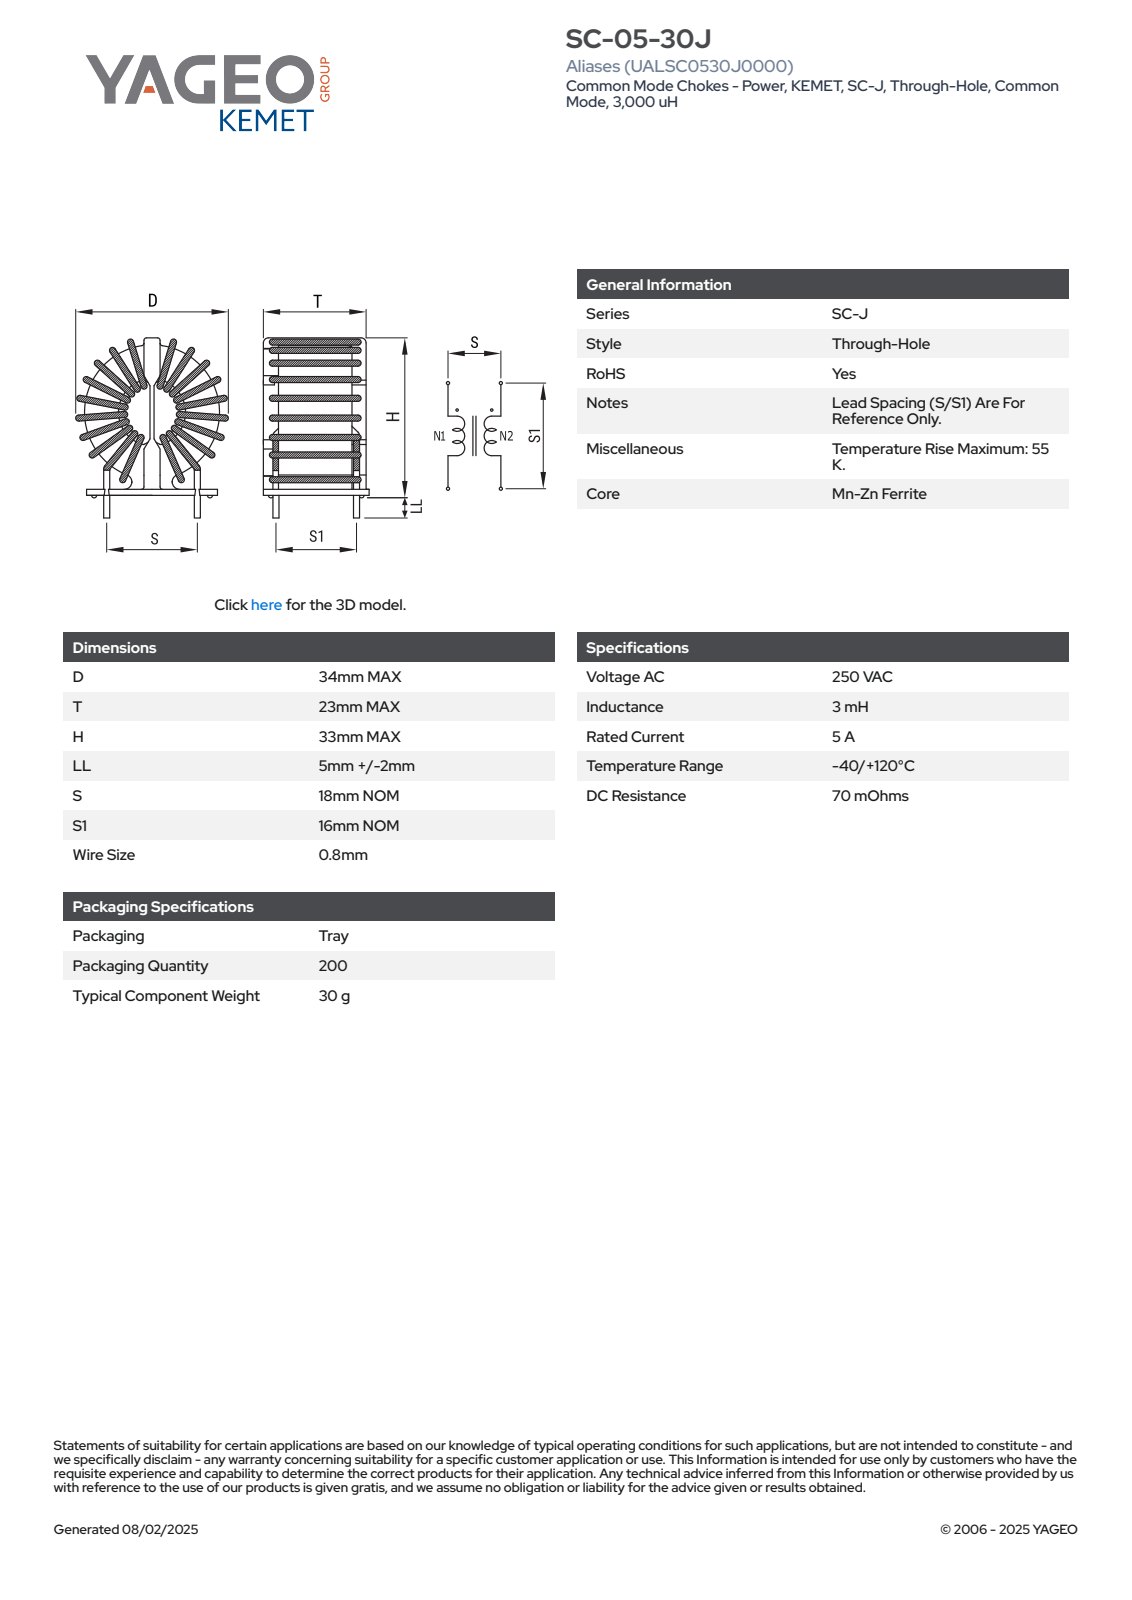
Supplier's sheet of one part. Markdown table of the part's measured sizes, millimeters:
| quantity | value |
| --- | --- |
| part name | SC-05-30J |
| STEP written by | SolidWorks 2018 (AUTOMOTIVE_DESIGN) |
| units | millimeters |
| bodies | 1 solid, 393 faces (177 planar, 132 cylindrical, 84 other) |
| overall size | 38 × 34 × 23 |
| volume | 14 501 mm³ |
| surface area | 7 757 mm² |
| round holes (diameter × count) | 1 × 4 |
| round bosses / shafts (diameter × count) | 0.8 × 8, 1 × 4 |
| partial cylindrical surfaces (radius × count) | 0.5 × 22, 0.4 × 16, 1 × 6, 0.7 × 4, 1.5 × 4, 4.5 × 1, 6.64 × 1, 7.35 × 1 |
| main face-to-face distances | 1.2, 19, 0.8, 16.8, 2, 2.2, 12.1, 3, 14.6, 1.6 |
| hole center spacings | 16, 18, 24.08 |
